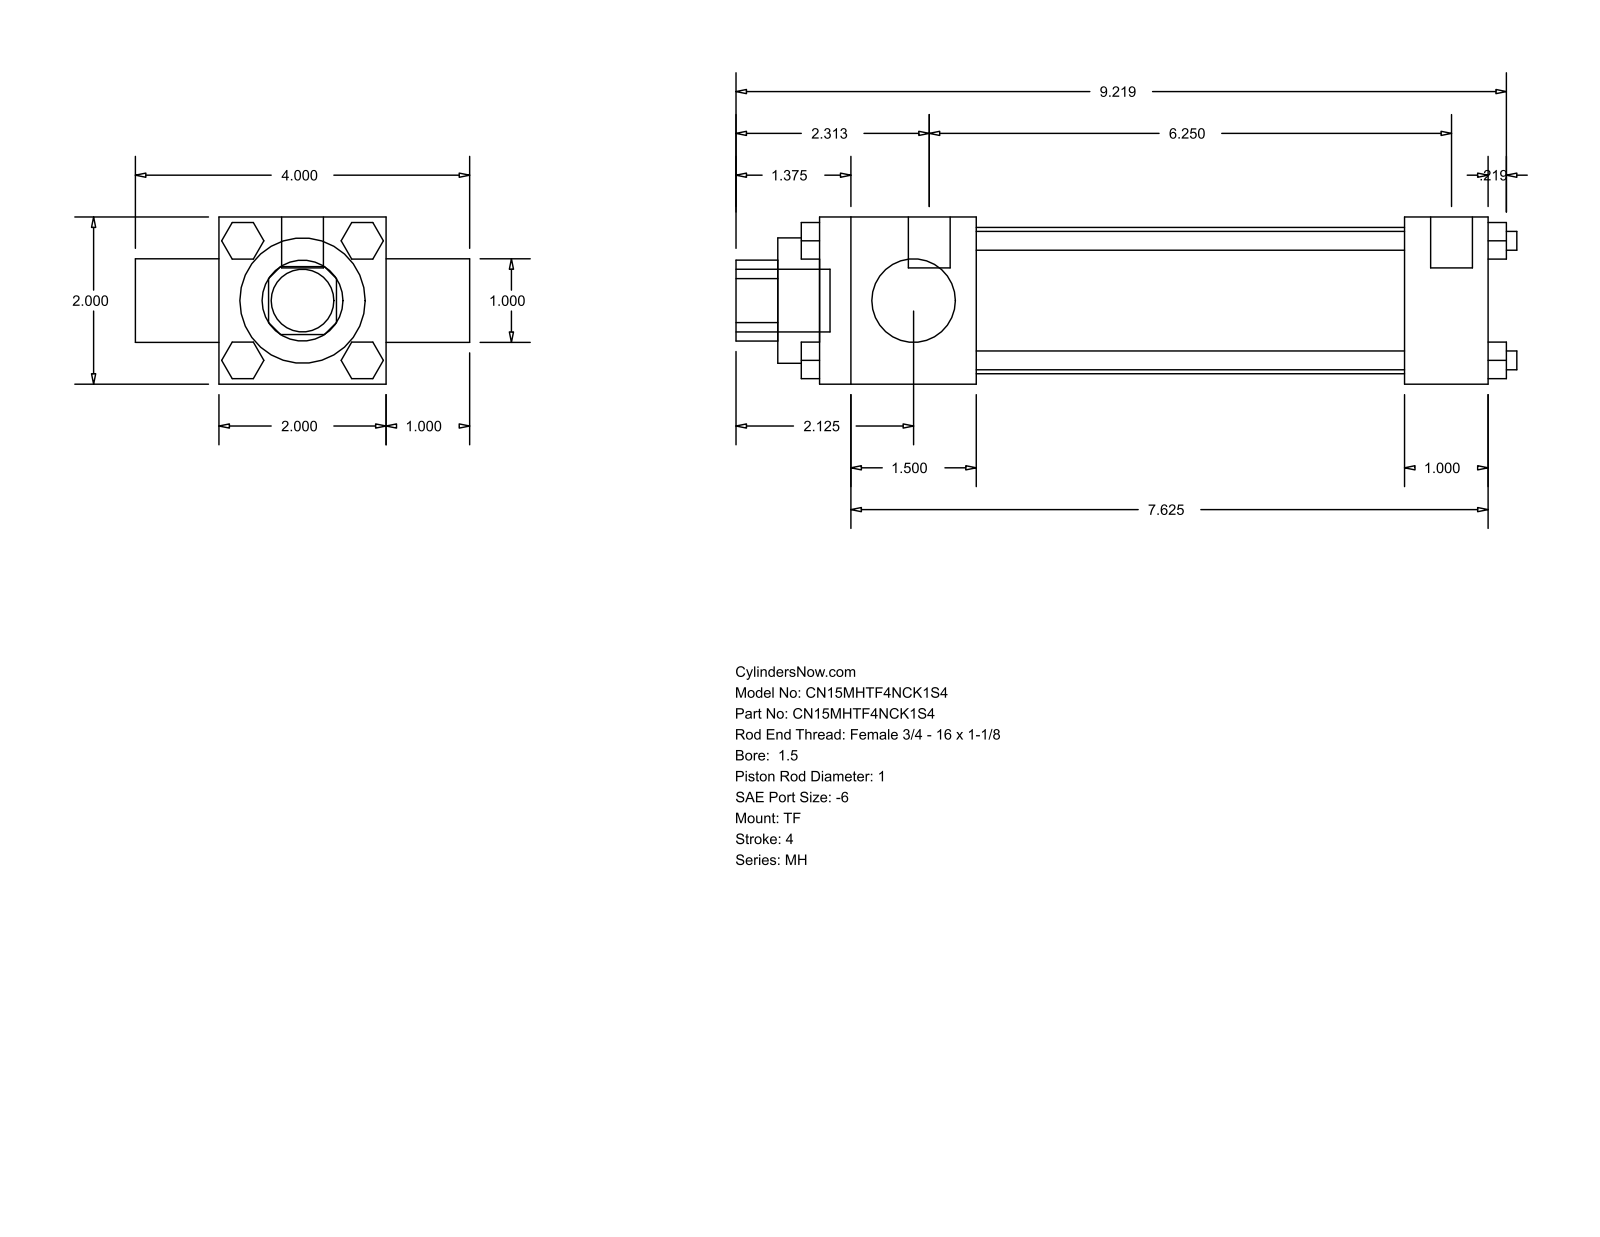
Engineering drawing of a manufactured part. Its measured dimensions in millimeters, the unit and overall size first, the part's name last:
Units: millimetres
Overall size (bounding box): 237.33 × 101.6 × 50.8
Round holes (diameter × count): ⌀25.4 ×2, ⌀38.1 ×1, ⌀44.45 ×1
Round bosses / shafts (diameter × count): ⌀5.71 ×4, ⌀5.56 ×3, ⌀12.7 ×2, ⌀19.05 ×1
Partial cylindrical surfaces — rounded edges, fillets, slot ends (radius × count): R12.29 ×1
Main face-to-face distances: 50.8, 25.4, 203.2, 76.2, 47.63, 155.57, 177.8, 130.17, 208.76, 12.7
Bodies: 0 solids, 120 faces (92 planar, 28 cylindrical, 0 other)
Part name (STEP PRODUCT): MH_TF__0150_1
STEP written by: GSSL Pune (CONFIG_CONTROL_DESIGN)
